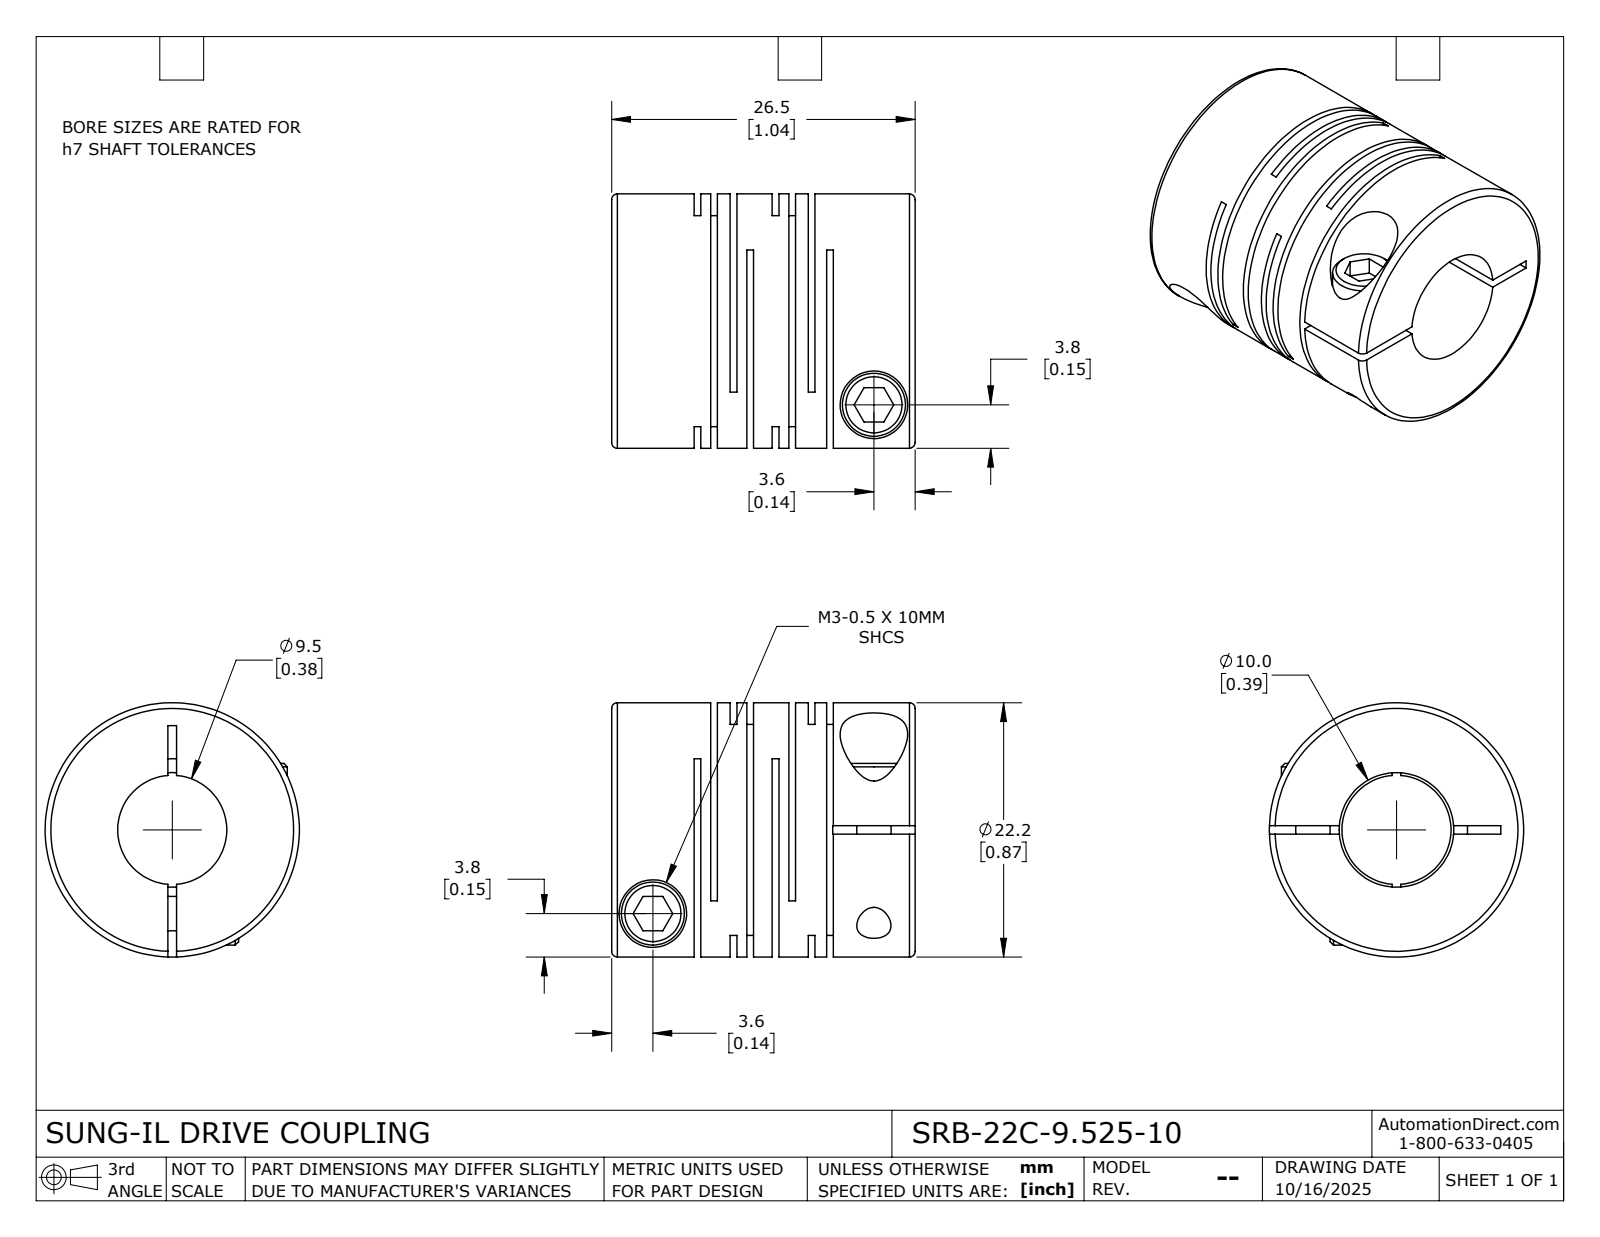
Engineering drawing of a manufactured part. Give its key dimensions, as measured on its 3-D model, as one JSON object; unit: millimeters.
{"part_name": "SRB-22C-9.525-10", "step_written_by": "SolidWorks 2024 (CONFIG_CONTROL_DESIGN)", "units": "millimeters", "bodies": {"solids": 1, "faces": 115, "planar": 60, "cylindrical": 42, "other": 13}, "overall_size": [26.5, 22.2, 22.2], "volume_mm3": 6772, "surface_area_mm2": 7427, "round_holes": [[3, 2], [5.9, 2], [9.53, 1], [10, 1]], "round_bosses_or_shafts": [[5.5, 2], [22.2, 1]], "face_to_face_distances": [0.59, 3.15, 6.82, 1.45, 5.37, 3.67, 1.7, 2.04, 3.74, 7.41]}
